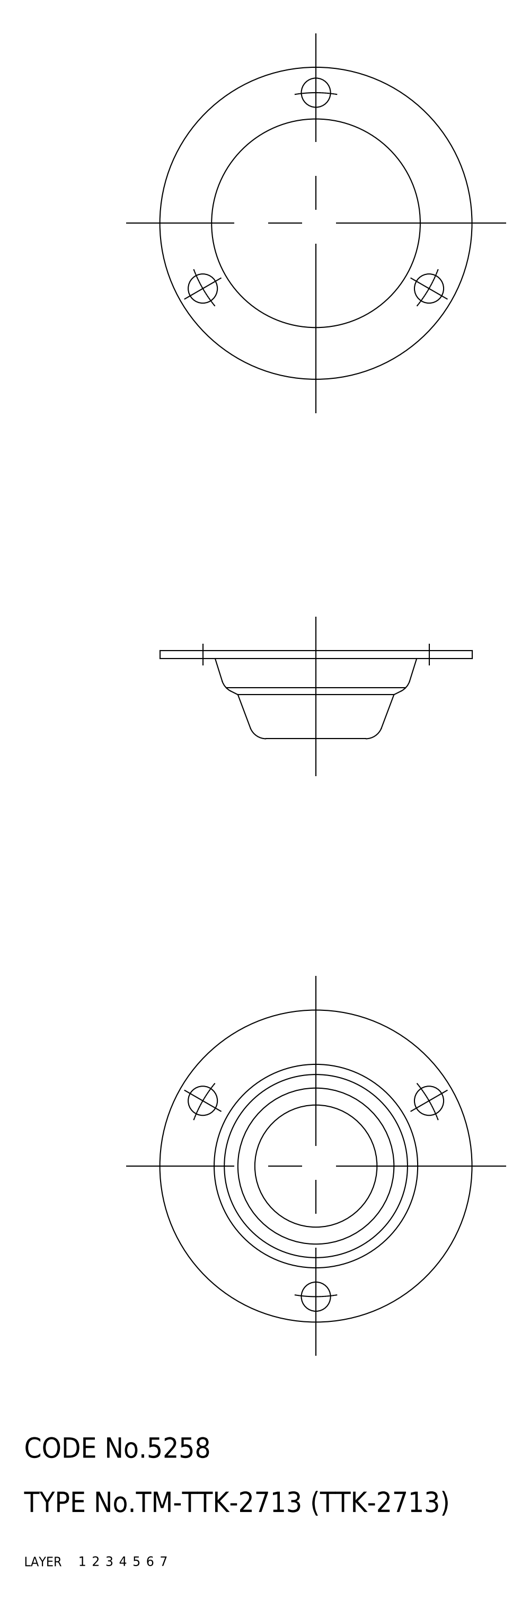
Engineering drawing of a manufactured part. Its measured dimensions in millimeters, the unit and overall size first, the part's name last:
Units: millimetres
Overall size (bounding box): 46 × 46 × 13
Volume: 7 397 mm³ · Surface area: 5 188 mm²
Bodies: 2 solids, 42 faces (0 planar, 0 cylindrical, 42 other)
Part name (STEP PRODUCT): rubber foot; bracket; TTK_2713_10716_36
STEP written by: CADfix (AUTOMOTIVE_DESIGN)
